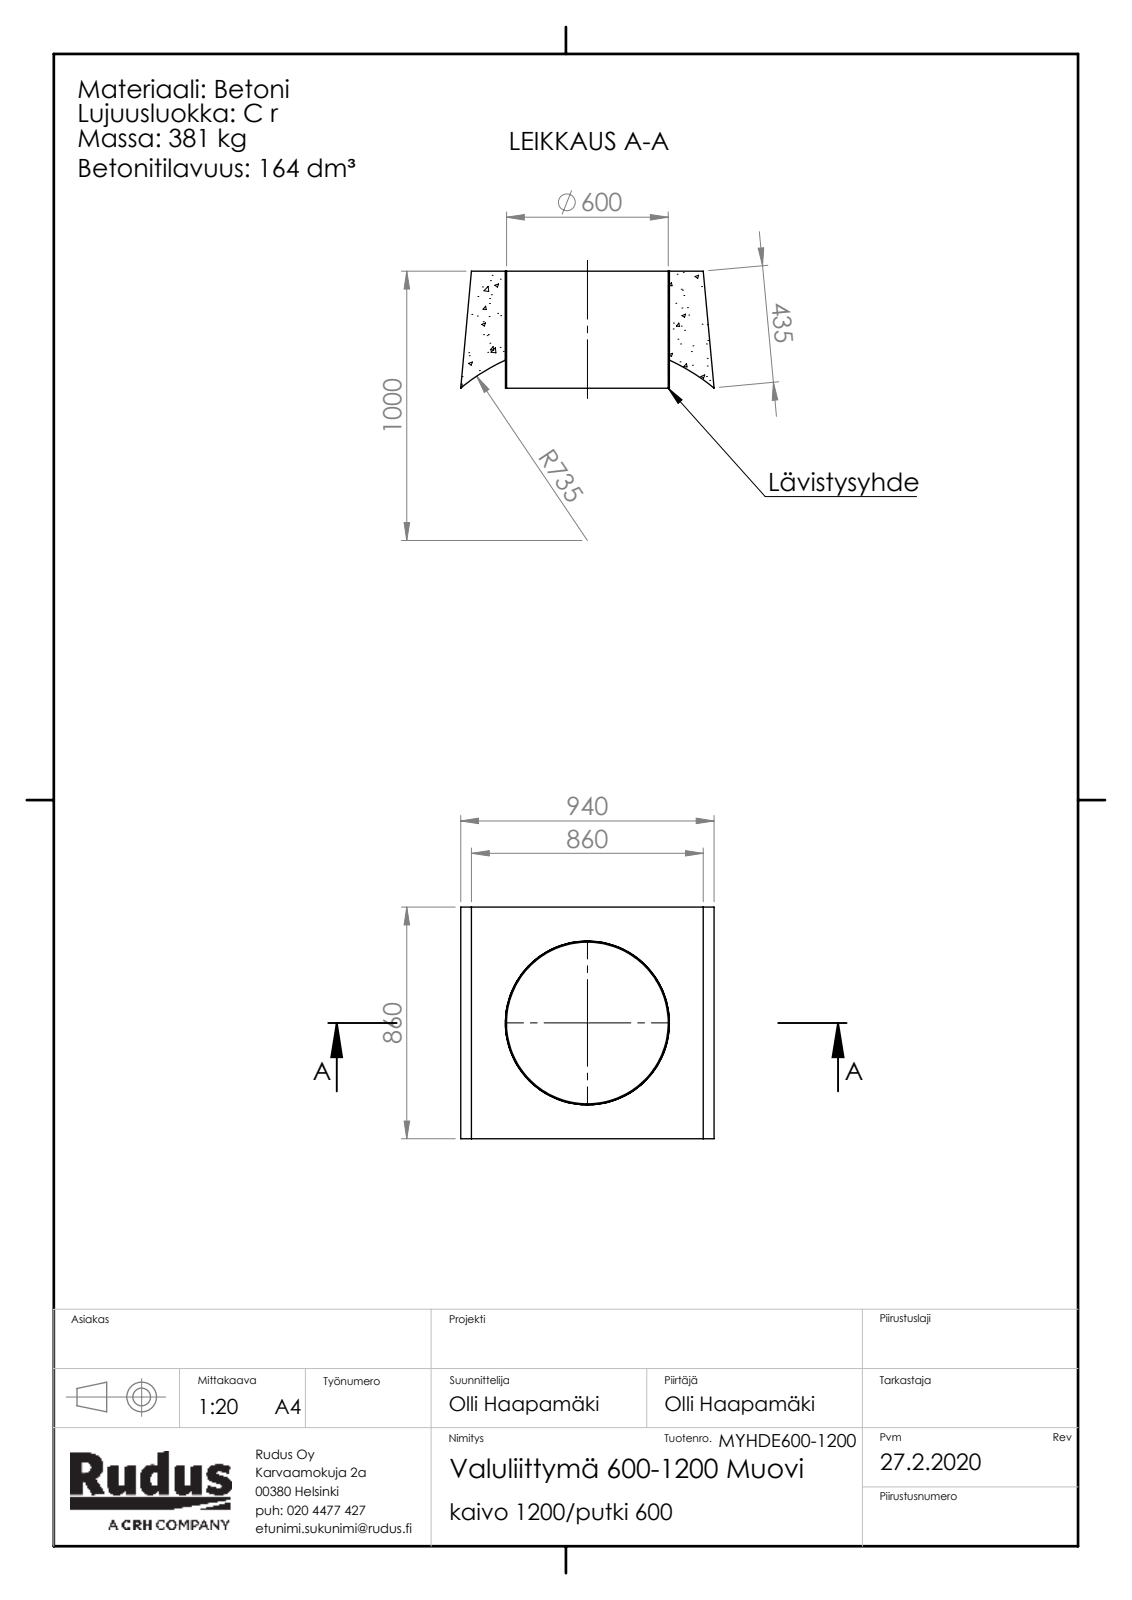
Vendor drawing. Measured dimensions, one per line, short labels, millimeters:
name: muovi-lavistysyhde; kaivo-osa-valuliittyma-runko_muovi; Rudus MYHDE600-1200 Valuliittymä 600-1200 Muovi
written by: SolidWorks 2019 (CONFIG_CONTROL_DESIGN)
unit: mm
bodies: 2 solids, 16 faces (9 planar, 7 cylindrical, 0 other)
size: 940 × 860 × 435
volume: 164 200 000 mm³; area: 4 575 000 mm²
holes: 1× ⌀600, 1× ⌀608
rounds: 1× R735
face distances: 860, 435
